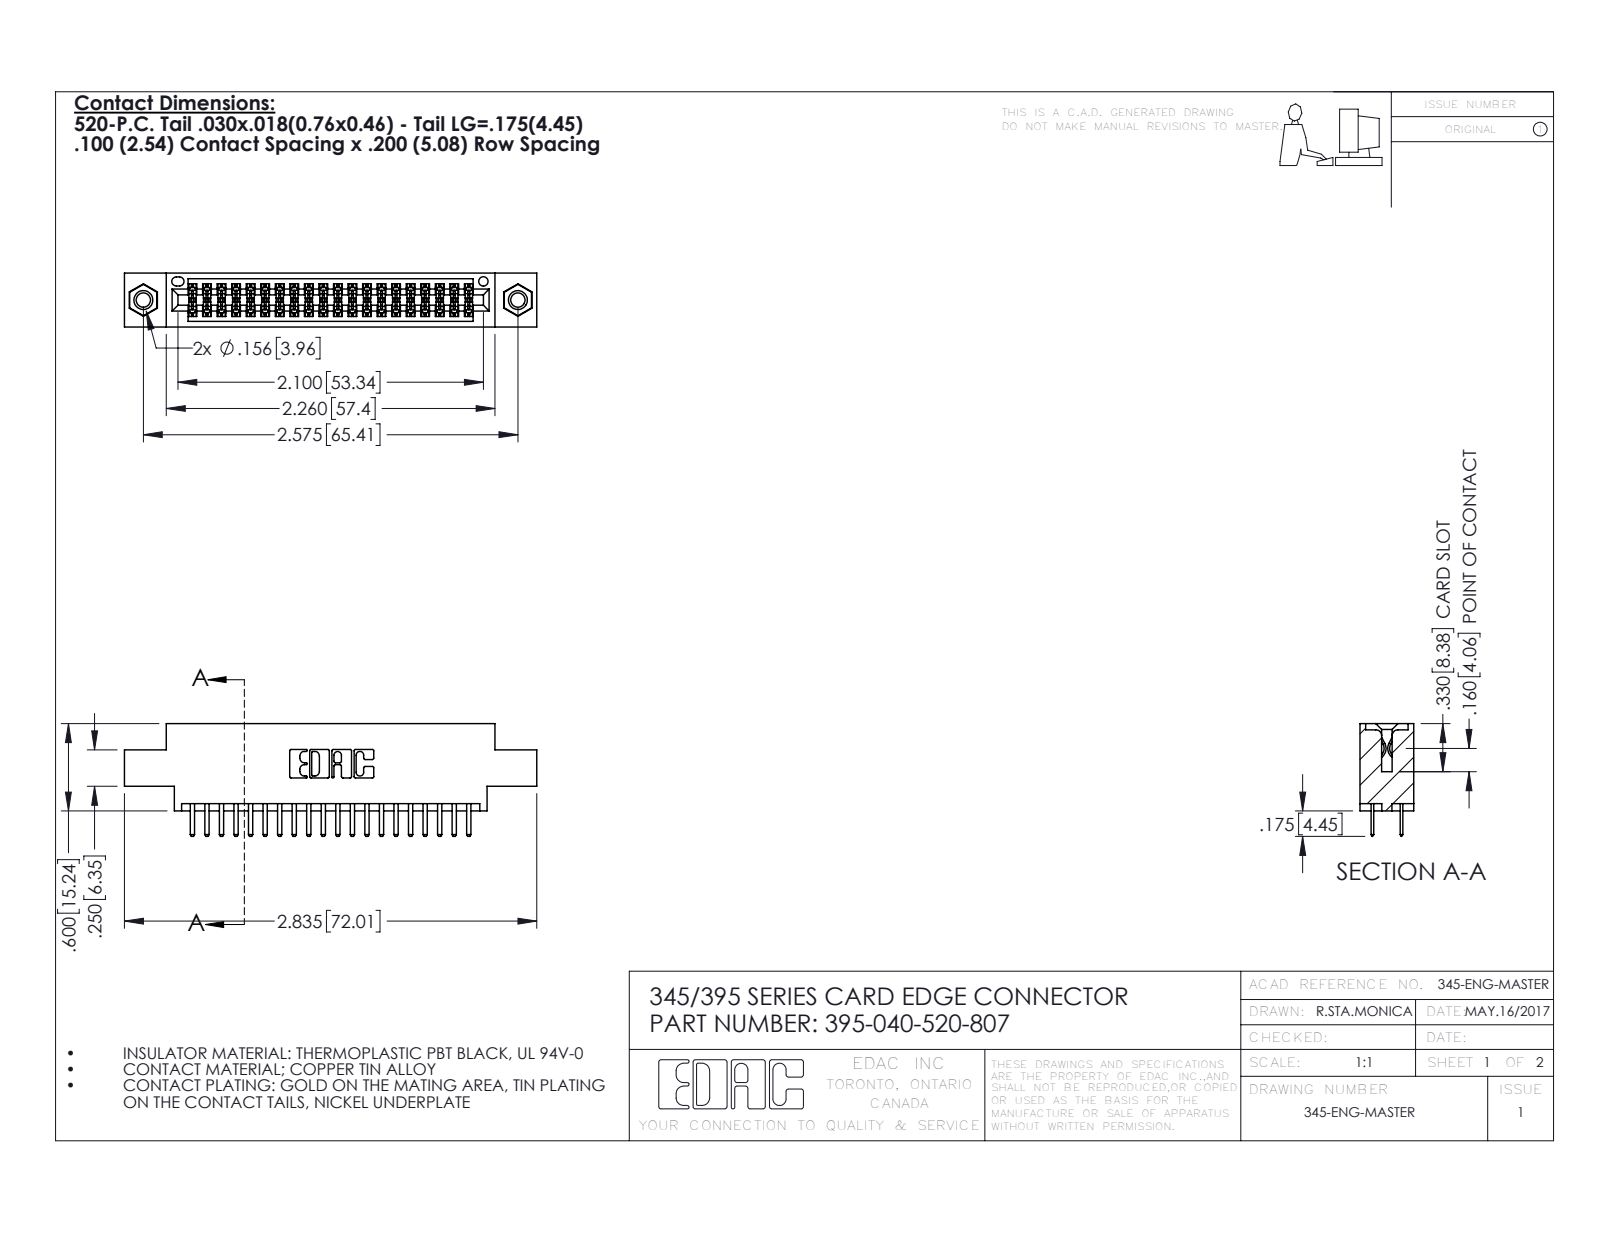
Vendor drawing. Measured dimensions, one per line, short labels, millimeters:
name: 345-250-001_345-250-005-103; 345-292-001_345-293-120; 345 Part_0.170 Offset - 0.156 Dia-TI; 395-040-520-807
written by: SolidWorks 2016 (CONFIG_CONTROL_DESIGN)
unit: mm
bodies: 43 solids, 2350 faces (1516 planar, 818 cylindrical, 16 other)
size: 72 × 19.7 × 9.4
volume: 6 650 mm³; area: 9 535 mm²
holes: 2× ⌀2.5, 2× ⌀3.2, 2× ⌀4, 1× ⌀1.6
bosses: 2× ⌀3.9
rounds: 60× R0.2, 44× R0.3, 22× R0.3, 6× R0.2, 6× R0.8, 3× R0.7, 2× R0.4, 2× R0.5
face distances: 1.8, 7.6, 5.1, 9.4, 2.5, 6.9, 0.6, 5.7, 0.6, 4.4
hole spacings: 6.9, 59.5, 65.4
